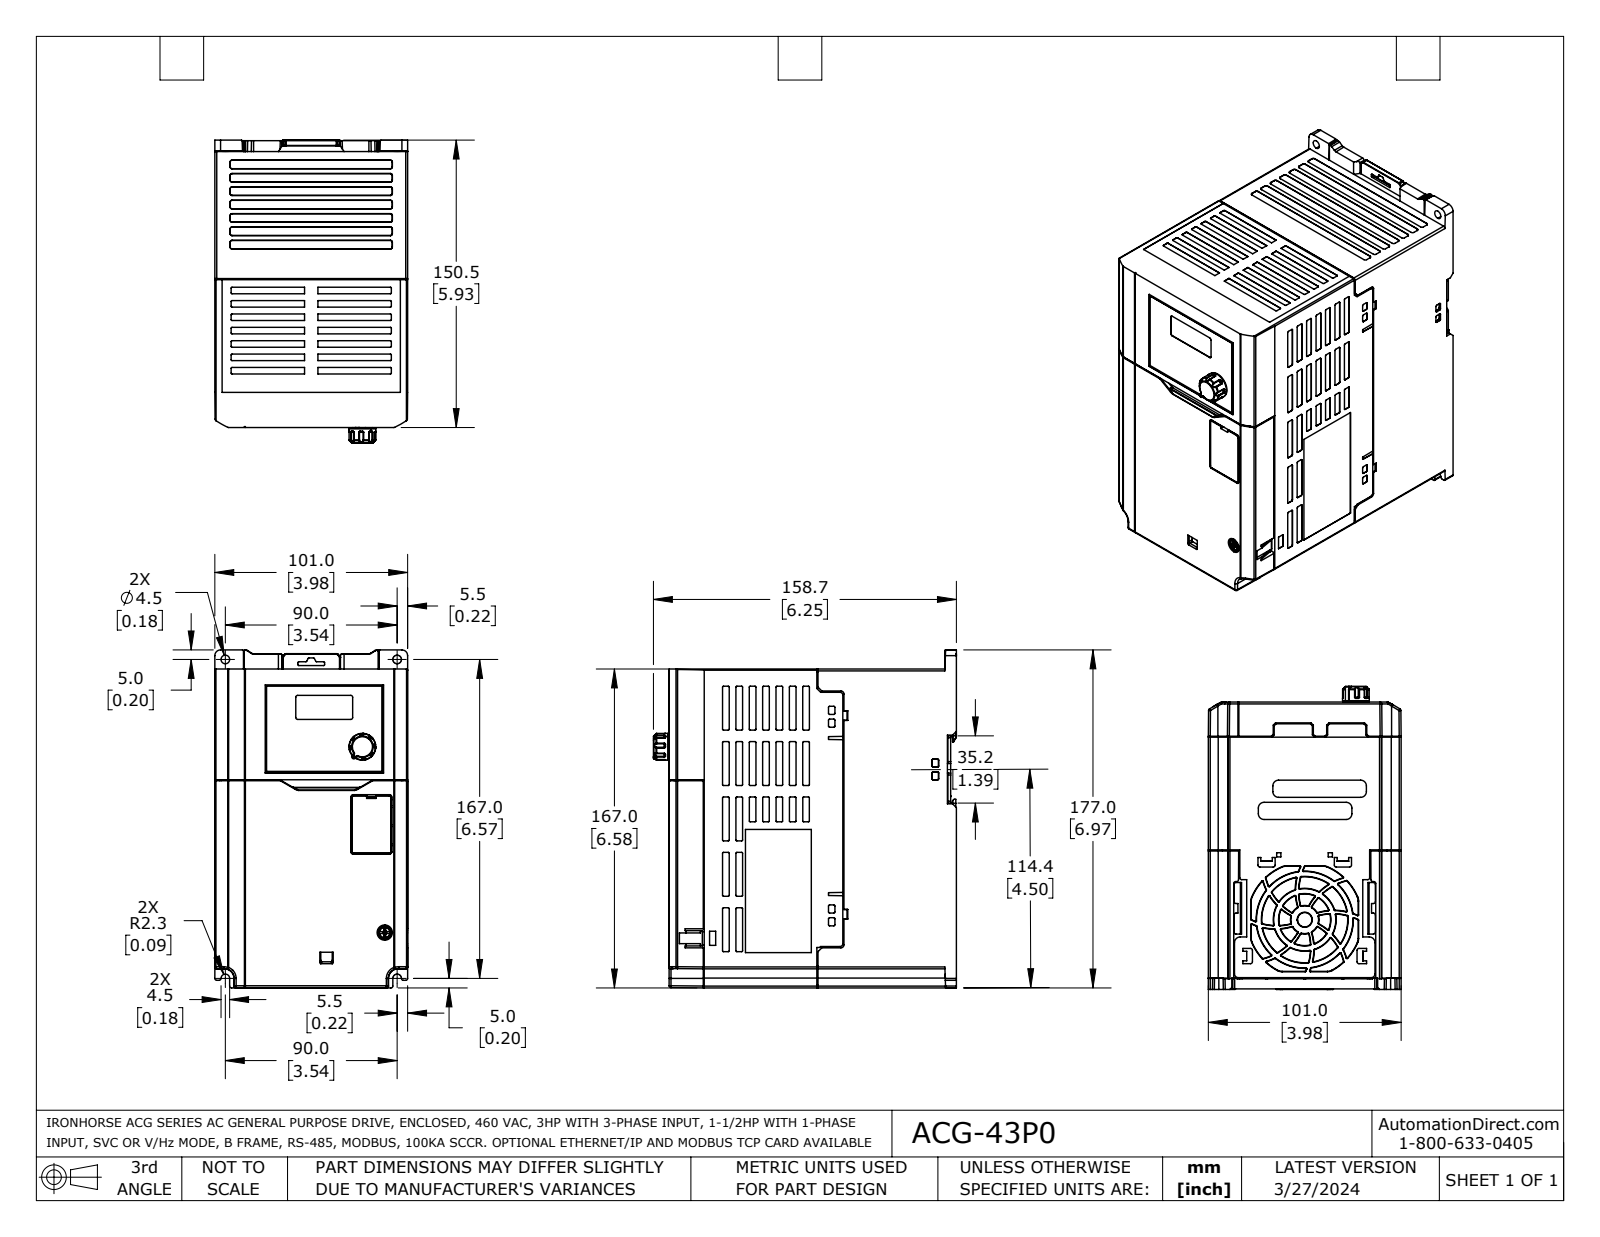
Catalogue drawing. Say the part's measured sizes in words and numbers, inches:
The part is named "ACG-43P0". Its 3-D file was written by "SolidWorks 2021 (AUTOMOTIVE_DESIGN)". It is 3 solids with 4587 faces: 1880 planar, 1198 cylindrical and 1509 other. Overall it measures 6.969 by 6.248 by 3.976 inches. Its volume is 150.3 cubic inches and its surface area 234.5 square inches. Round holes: 4 of diameter 0.134, 1 of diameter 0.039, 1 of diameter 0.276, 1 of diameter 0.472. Round bosses or shafts: 1 of diameter 0.551, 1 of diameter 0.543, 1 of diameter 0.236. Partial cylindrical surfaces (rounded edges, fillets, slot ends): 347 of radius 0.008, 240 of radius 0.02, 95 of radius 0.039, 38 of radius 0.018, 24 of radius 0.012, 17 of radius 0.031, 12 of radius 0.118, 4 of radius 0.016. The main face-to-face distances are 3.976, 5.807, 3.975, 6.575, 5.795, 6.573, 0.106, 5.913, 0.118, 0.098. The hole center spacings are 3.496, 4.882, 6.005, 0.276, 0.491, 0.928, 1.202, 2.754.
